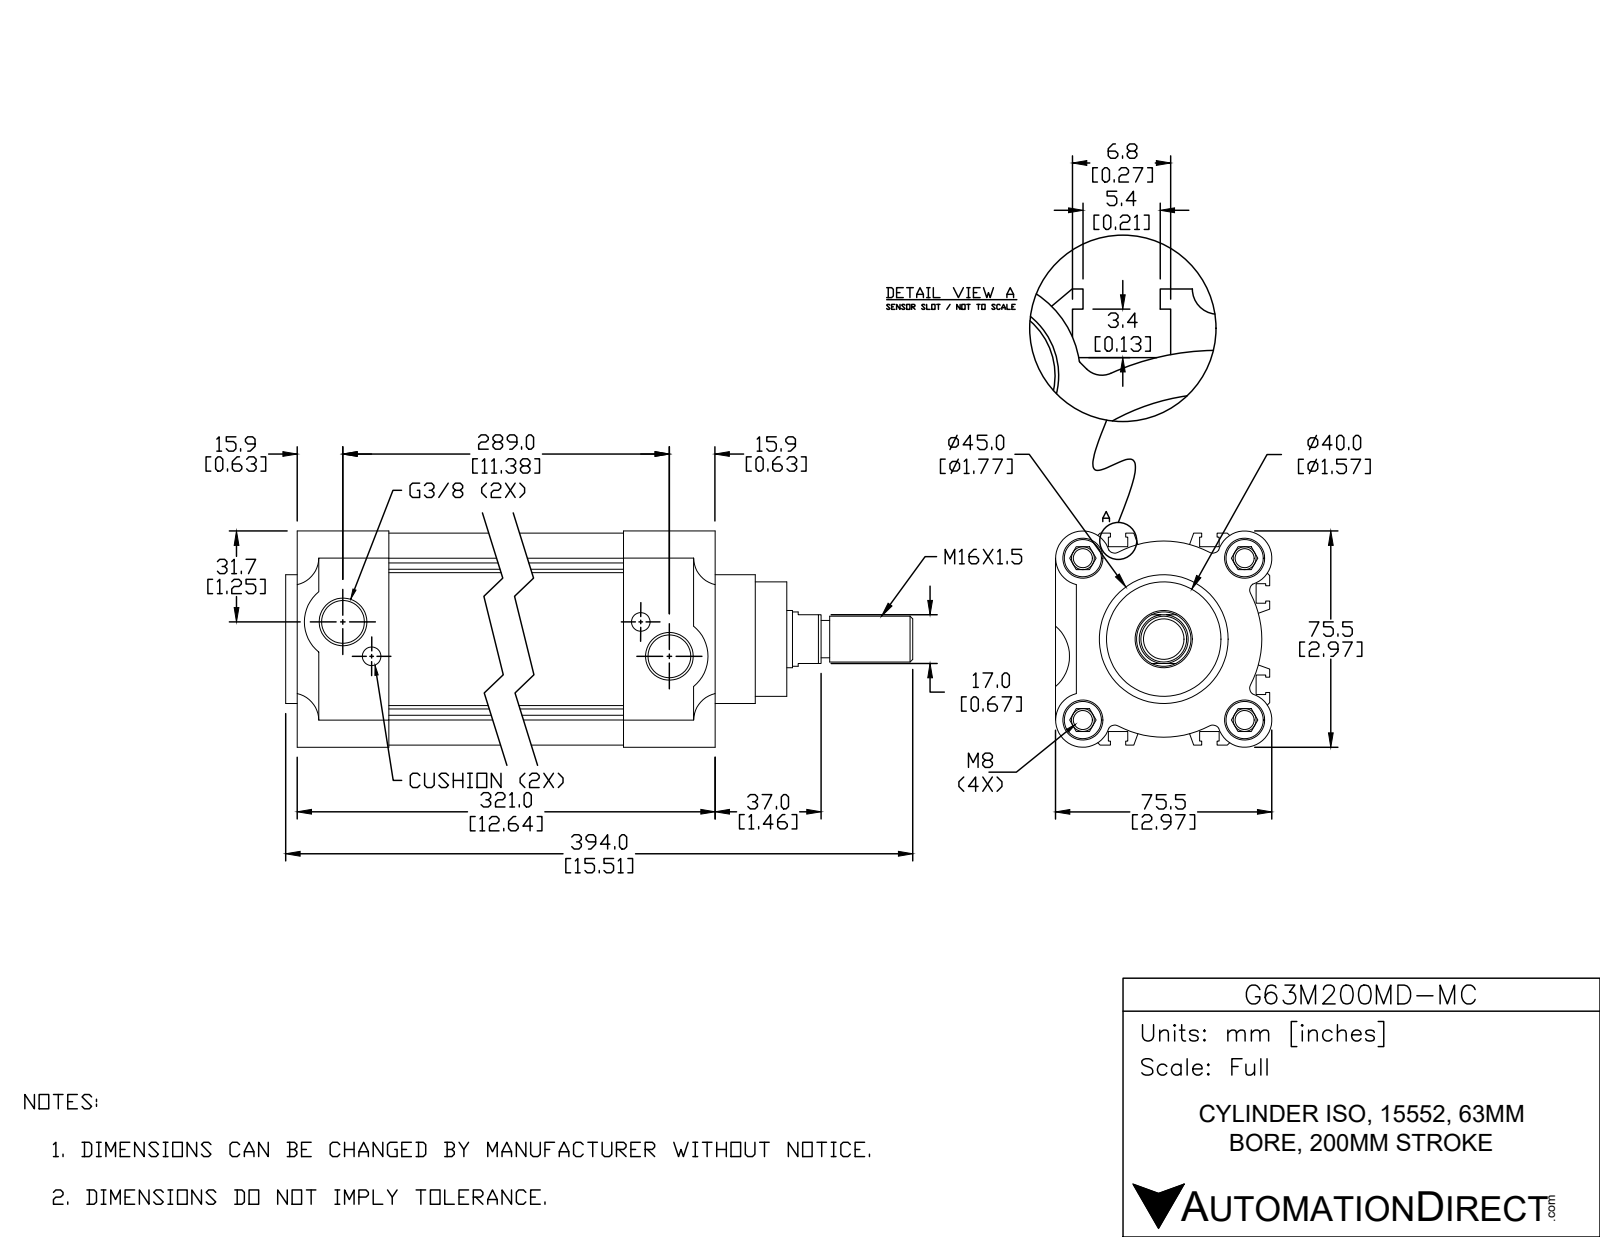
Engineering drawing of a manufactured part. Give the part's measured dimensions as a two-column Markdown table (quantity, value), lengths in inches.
| quantity | value |
| --- | --- |
| part name | 63121200-R; 63-200-98-B; 63121-HR; 63-HL (+1 more) |
| STEP written by | SolidWorks 2015 (CONFIG_CONTROL_DESIGN) |
| units | inches |
| bodies | 4 solids, 422 faces (240 planar, 138 cylindrical, 44 other) |
| overall size | 15.512 × 2.974 × 2.972 |
| volume | 64.69 in³ |
| surface area | 399.2 in² |
| round holes (diameter × count) | 0.262 × 4, 0.551 × 4, 0.256 × 2, 0.262 × 2, 0.589 × 2, 0.787 × 1 |
| round bosses / shafts (diameter × count) | 0.512 × 5, 2.48 × 1, 1.772 × 1, 1.575 × 1, 0.748 × 1, 0.63 × 1 |
| partial cylindrical surfaces (radius × count) | 0.004 × 6, 0.098 × 6, 0.344 × 4, 0.374 × 4, 0.531 × 2, 1.339 × 1, 1.348 × 1 |
| main face-to-face distances | 0.187, 2.726, 1.256, 0.354, 9.764, 1.937, 1.359, 0.268, 2.913, 1.26 |
| hole center spacings | 1.573, 2.224, 0.615, 3.146, 10.984, 10.601, 11.388 |
